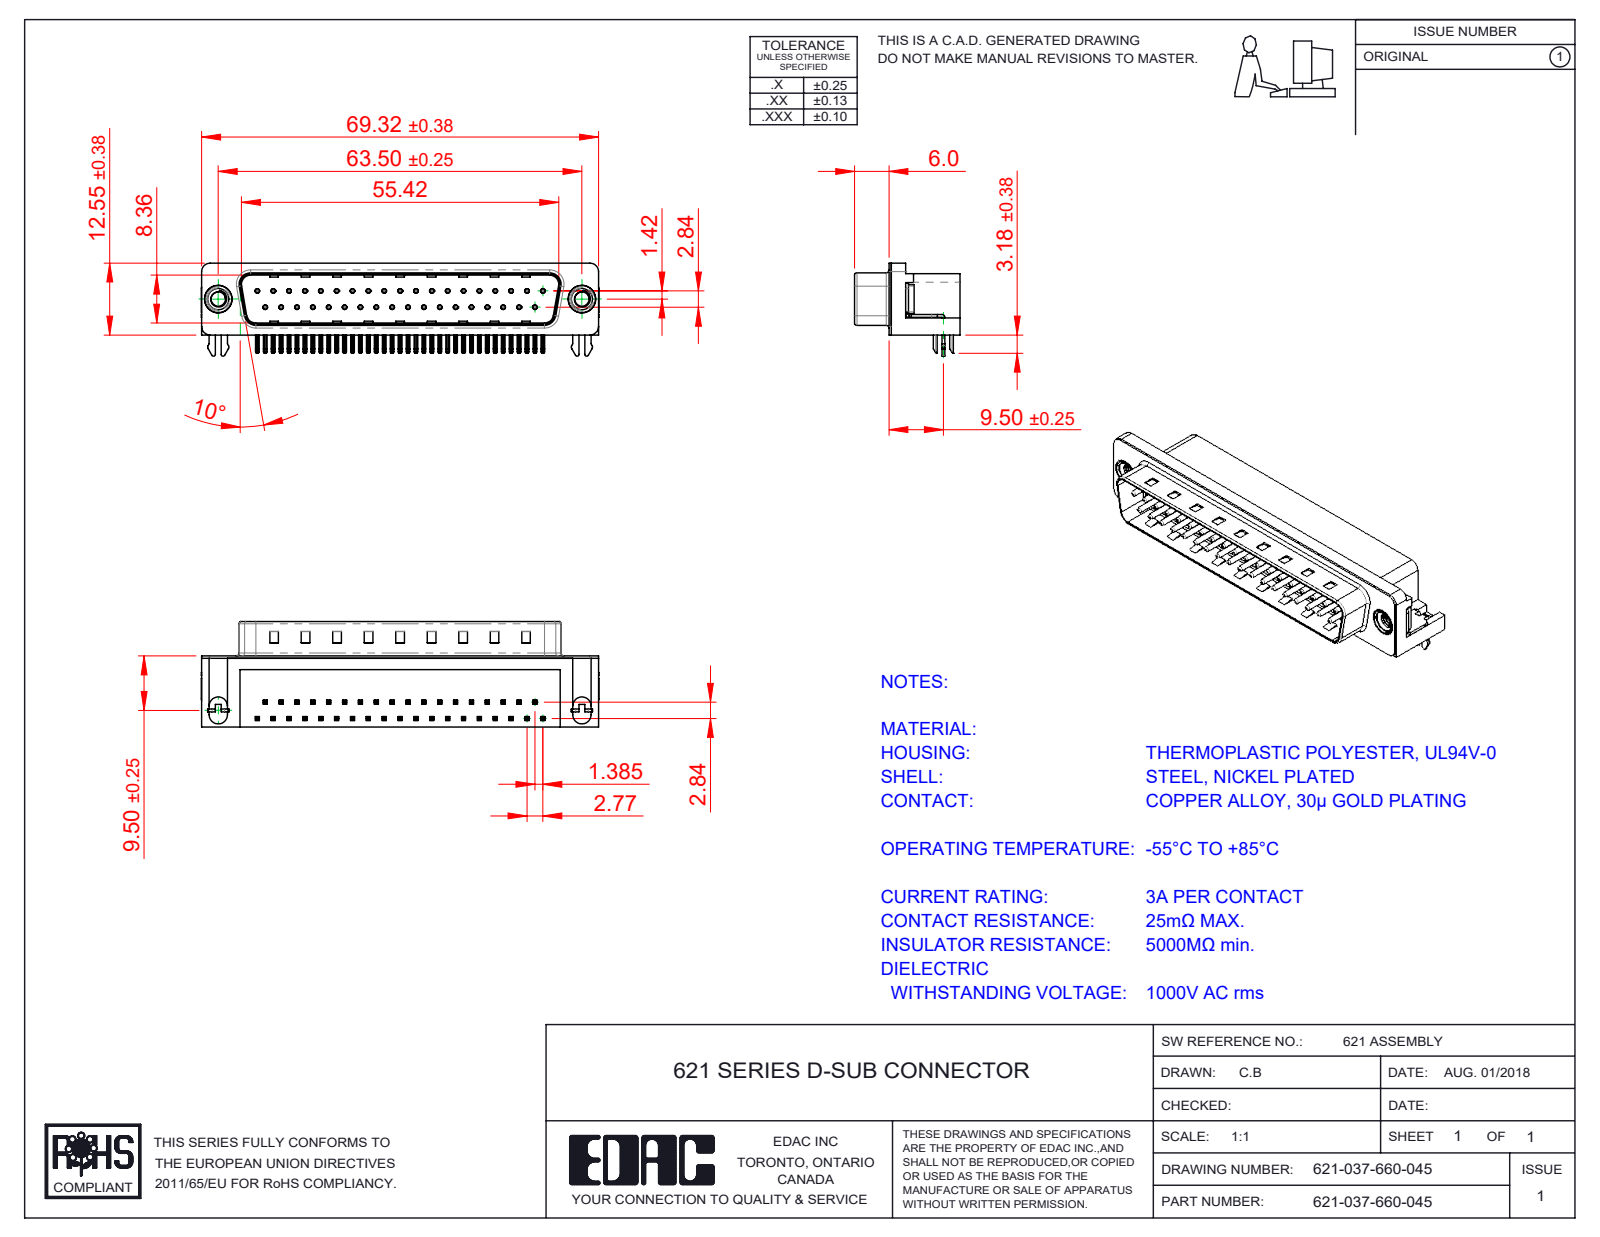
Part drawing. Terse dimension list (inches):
name: 621 M3 Threaded Rivet; 621-037-660-045; 621 Contact Bottom; 621 Shell_37 Socket (+3 more)
written by: SolidWorks 2016 (CONFIG_CONTROL_DESIGN)
unit: in
bodies: 43 solids, 3319 faces (2055 planar, 925 cylindrical, 339 other)
size: 2.732 × 0.724 × 0.64
volume: 0.526 in³; area: 15.77 in²
holes: 37× ⌀0.014, 37× ⌀0.031, 2× ⌀0.079, 2× ⌀0.098, 2× ⌀0.157, 2× ⌀0.189, 2× ⌀0.197
bosses: 37× ⌀0.03, 2× ⌀0.193, 2× ⌀0.187, 2× ⌀0.154, 2× ⌀0.118
rounds: 160× R0.01, 74× R0.005, 16× R0.039, 9× R0.02, 8× R0.063, 7× R0.059, 4× R0.035, 4× R0.079
face distances: 0.016, 0.472, 0.407, 0.345, 0.083, 0.067, 0.412, 0.428, 0.354, 0.488
hole spacings: 0.124, 0.109, 0.218, 0.327, 0.436, 0.545, 0.763, 0.872
